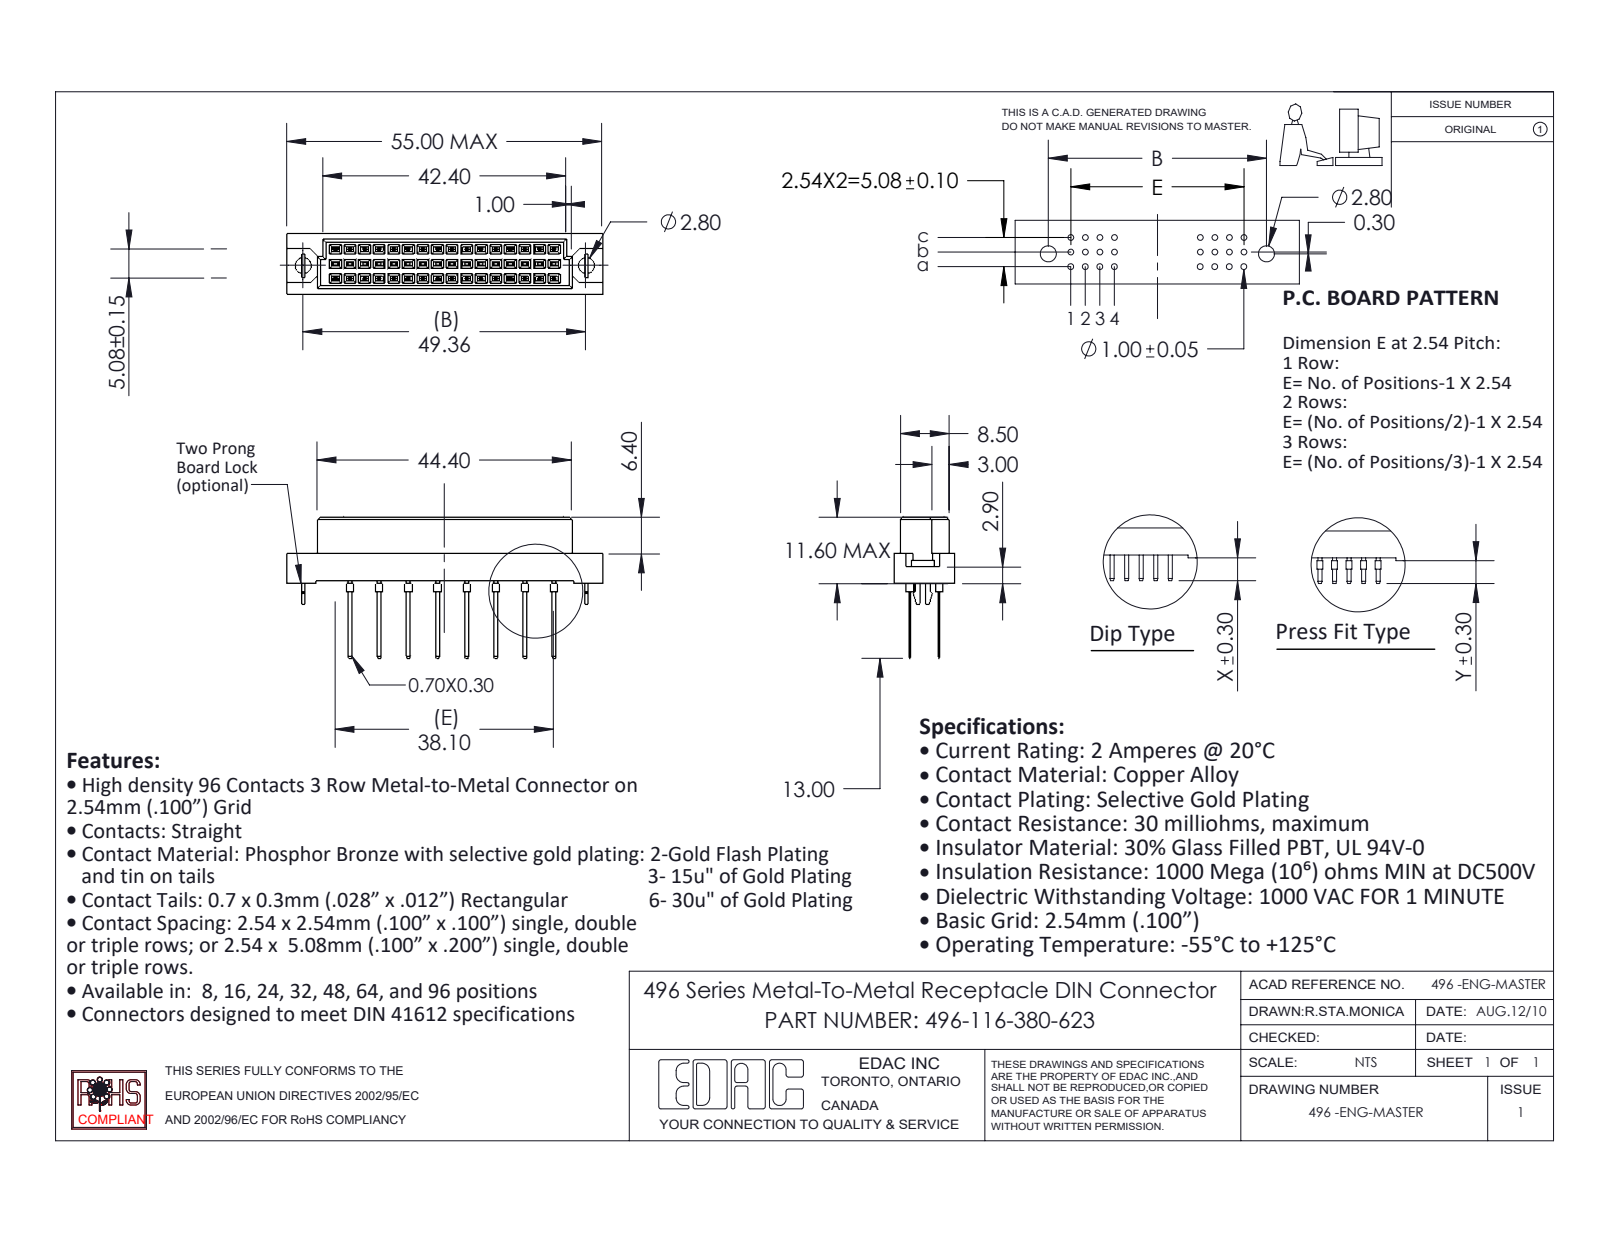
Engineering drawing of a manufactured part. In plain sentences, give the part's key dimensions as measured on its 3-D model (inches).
The part is named "496-116-380-623; 496 Part_48; 496 Bore-lock; 496-290_80". Its 3-D file was written by "SolidWorks 2020 (CONFIG_CONTROL_DESIGN)". It is 19 solids with 990 faces: 952 planar, 38 cylindrical and 0 other. Overall it measures 2.165 by 0.969 by 0.417 inches. Its volume is 0.286 cubic inches and its surface area 7.649 square inches. Round holes: 2 of diameter 0.11. Round bosses or shafts: 16 of diameter 0.039. Partial cylindrical surfaces (rounded edges, fillets, slot ends): 1 of radius 0.021. The main face-to-face distances are 0.1, 0.2, 0.041, 0.376, 0.032, 0.022, 0.022, 0.061, 0.073, 0.103. The hole center spacings are 1.943.
